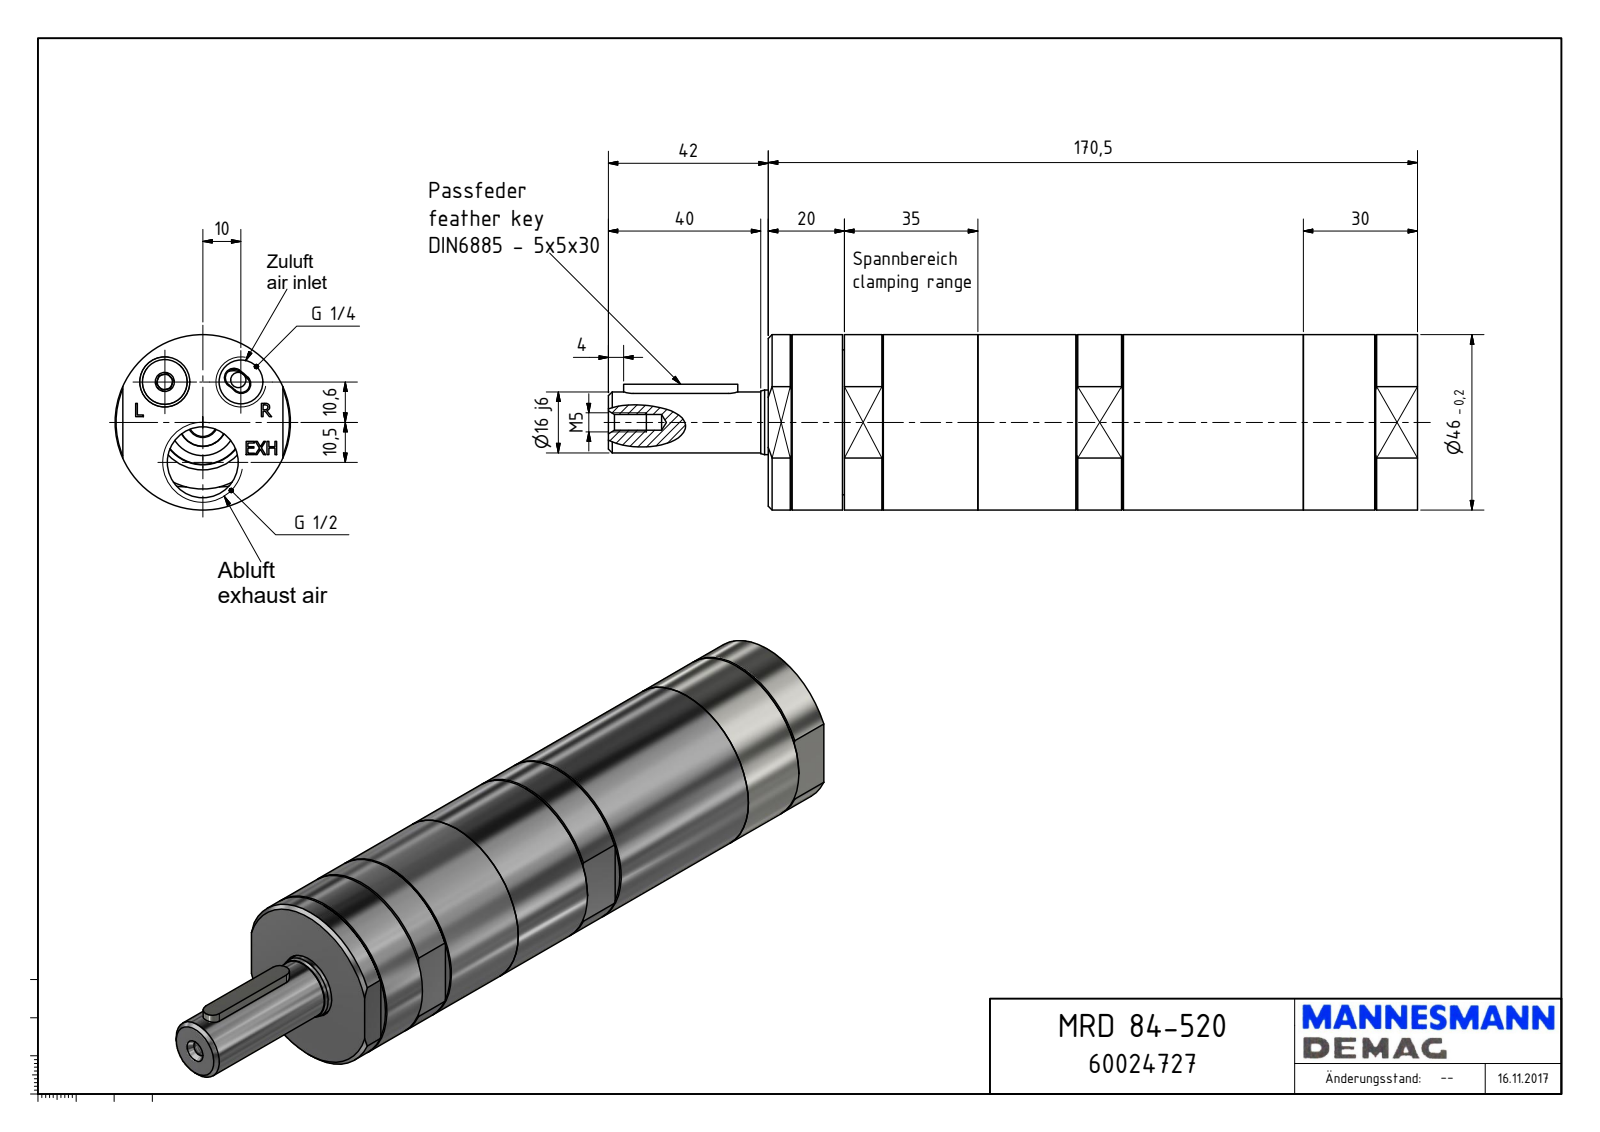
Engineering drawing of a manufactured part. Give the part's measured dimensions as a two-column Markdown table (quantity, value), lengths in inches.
| quantity | value |
| --- | --- |
| part name | MRD 84-520_60024727 |
| STEP written by | Autodesk Inventor 2018 (AUTOMOTIVE_DESIGN) |
| units | inches |
| bodies | 1 solid, 182 faces (110 planar, 36 cylindrical, 36 other) |
| overall size | 8.366 × 1.811 × 1.811 |
| volume | 17.41 in³ |
| surface area | 52.94 in² |
| round holes (diameter × count) | 0.157 × 1, 0.163 × 1, 0.451 × 1, 0.689 × 1, 0.733 × 1, 1.496 × 1, 1.511 × 1 |
| round bosses / shafts (diameter × count) | 1.811 × 1, 1.328 × 1, 0.667 × 1, 0.63 × 1 |
| partial cylindrical surfaces (radius × count) | 0.098 × 2, 0.197 × 2, 0.225 × 1, 0.259 × 1, 0.354 × 1 |
| main face-to-face distances | 6.713, 1.654, 6.387, 0.325, 0.787, 5.6, 5.925, 0.768, 0.02, 5.62 |
| hole center spacings | 0.574, 0.919, 0.413, 0.787 |
